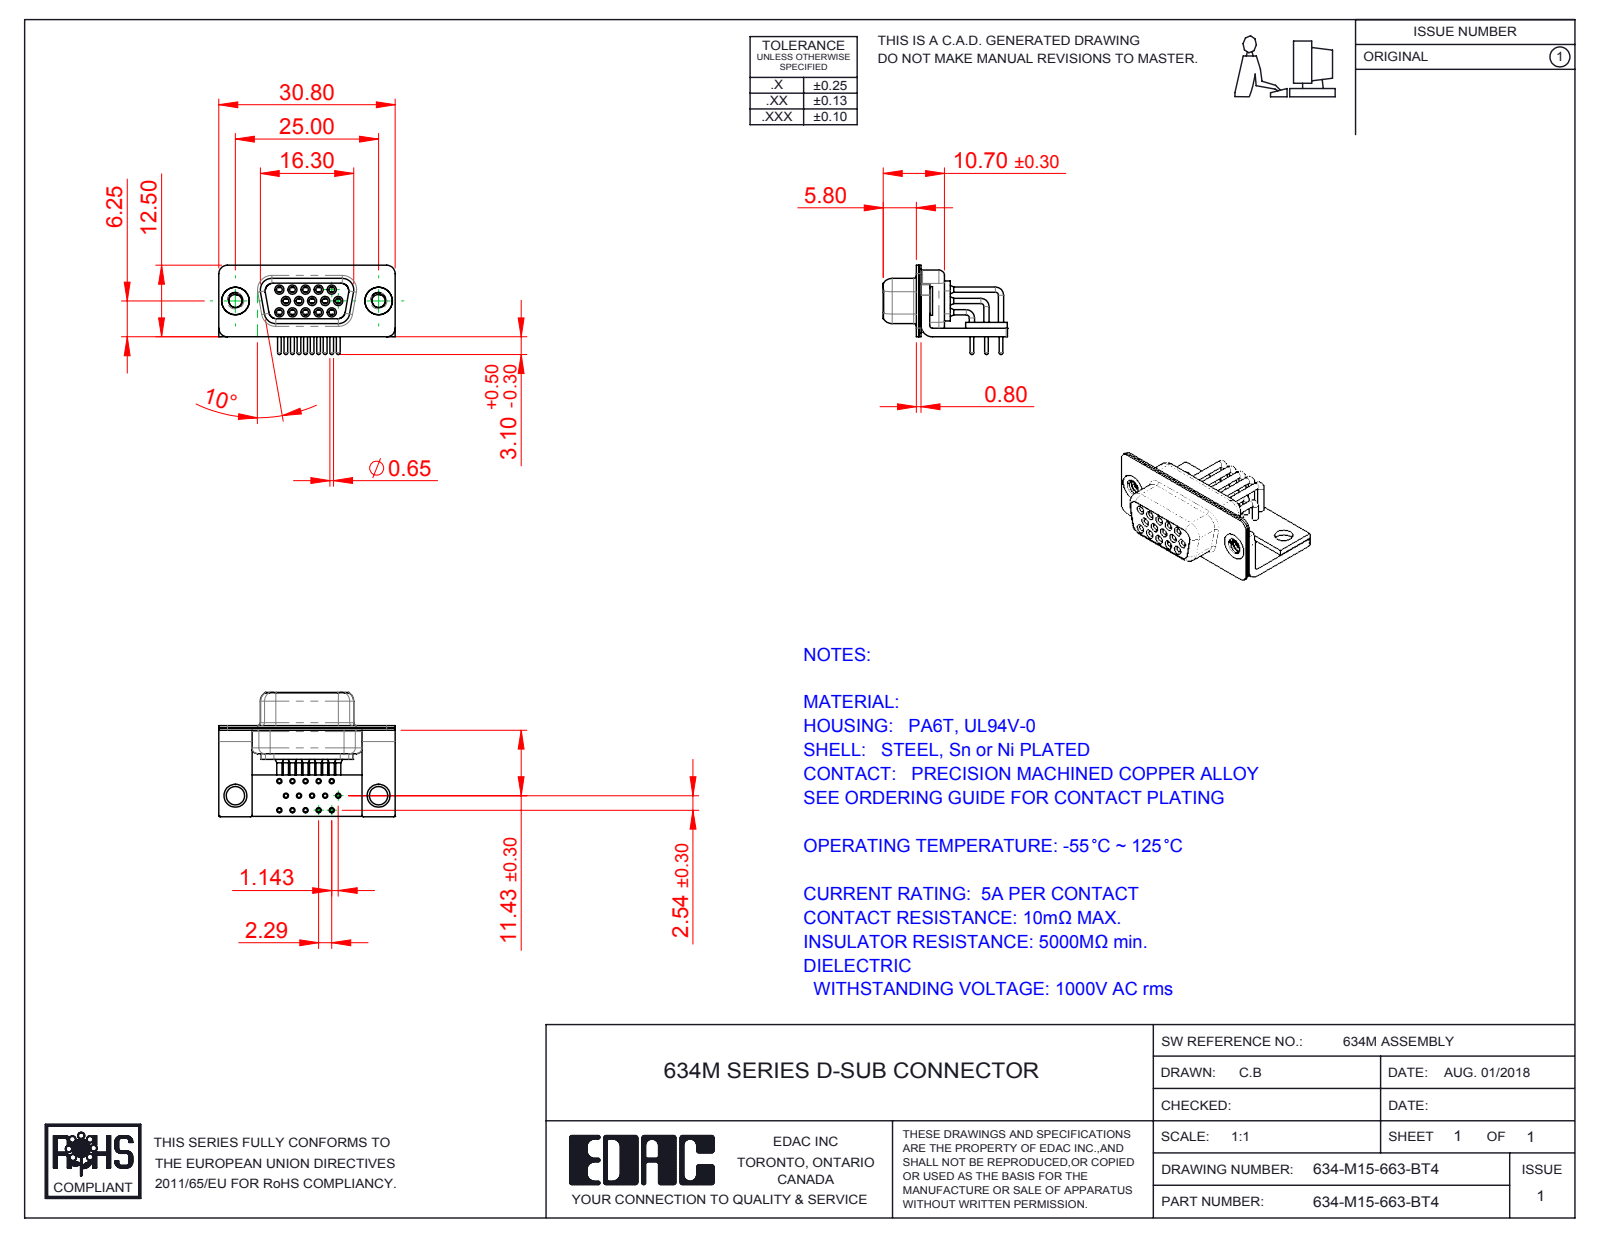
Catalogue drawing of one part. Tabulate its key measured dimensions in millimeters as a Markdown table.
| quantity | value |
| --- | --- |
| part name | 634-M15-663-BT4; 634M Shell Rear_15 Contacts; 634M Stabilizer Bracket; 634M Stabilizer Board_15 Contacts (+6 more) |
| STEP written by | SolidWorks 2016 (CONFIG_CONTROL_DESIGN) |
| units | millimeters |
| bodies | 23 solids, 1154 faces (318 planar, 534 cylindrical, 302 other) |
| overall size | 30.8 × 21.7 × 15.6 |
| volume | 2 216 mm³ |
| surface area | 6 817 mm² |
| round holes (diameter × count) | 0.9 × 15, 1 × 15, 1.1 × 15, 1.7 × 15, 1.8 × 15, 2 × 15, 2.26 × 2, 3.2 × 2, 4 × 2, 4.8 × 2 |
| round bosses / shafts (diameter × count) | 1.6 × 15, 1.5 × 15, 0.9 × 15, 0.65 × 15, 5 × 2, 4.9 × 2, 2 × 1 |
| partial cylindrical surfaces (radius × count) | 0.25 × 16, 1.5 × 16, 2 × 13, 1.35 × 8, 1.6 × 8, 0.5 × 5, 0.6 × 4, 0.65 × 4 |
| main face-to-face distances | 0.4, 0.8, 1.5, 1, 2.3, 1.9, 9.35, 2.5, 1.45, 0.85 |
| hole center spacings | 2.29, 2.28, 4.57, 3.96, 4.27, 2.78, 6.05, 6.86 |
